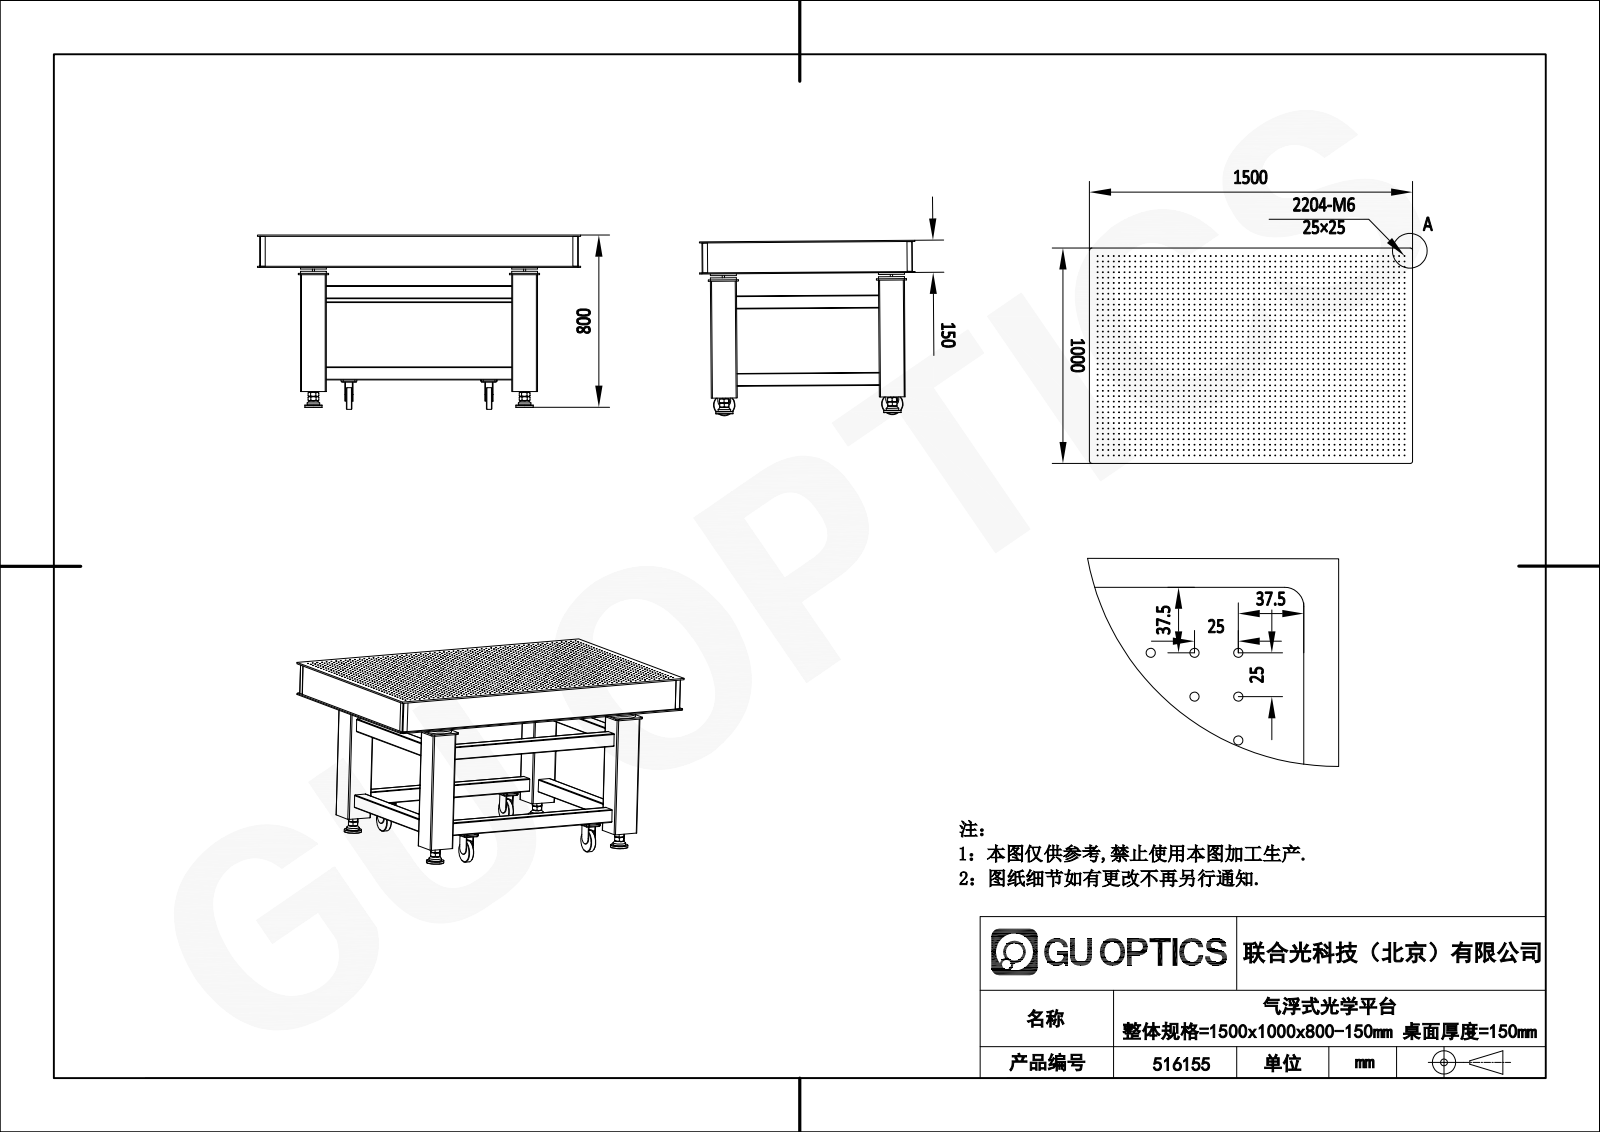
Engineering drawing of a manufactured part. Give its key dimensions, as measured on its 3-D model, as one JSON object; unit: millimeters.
{"part_name": "516155", "step_written_by": "SolidWorks 2020 (CONFIG_CONTROL_DESIGN)", "units": "millimeters", "bodies": {"solids": 62, "faces": 7653, "planar": 2693, "cylindrical": 4768, "other": 192}, "overall_size": [1500, 1000, 808], "volume_mm3": 225800000, "surface_area_mm2": 12740000, "round_holes": [[5.3, 2204], [8.5, 16], [9, 16], [17.5, 4], [22, 4], [28, 4], [43, 4]], "round_bosses_or_shafts": [[120, 4], [80, 4], [58, 4], [14, 4], [10, 4], [100, 2]], "partial_cylinders_radius": [[1, 48], [10, 48], [3, 36], [5, 16], [7, 16], [2, 4], [11, 4], [30, 2]], "face_to_face_distances": [5, 150, 145, 2, 58, 4, 116, 780, 28, 980], "hole_center_spacings": [50, 100, 150, 200, 250, 300, 350, 400]}
